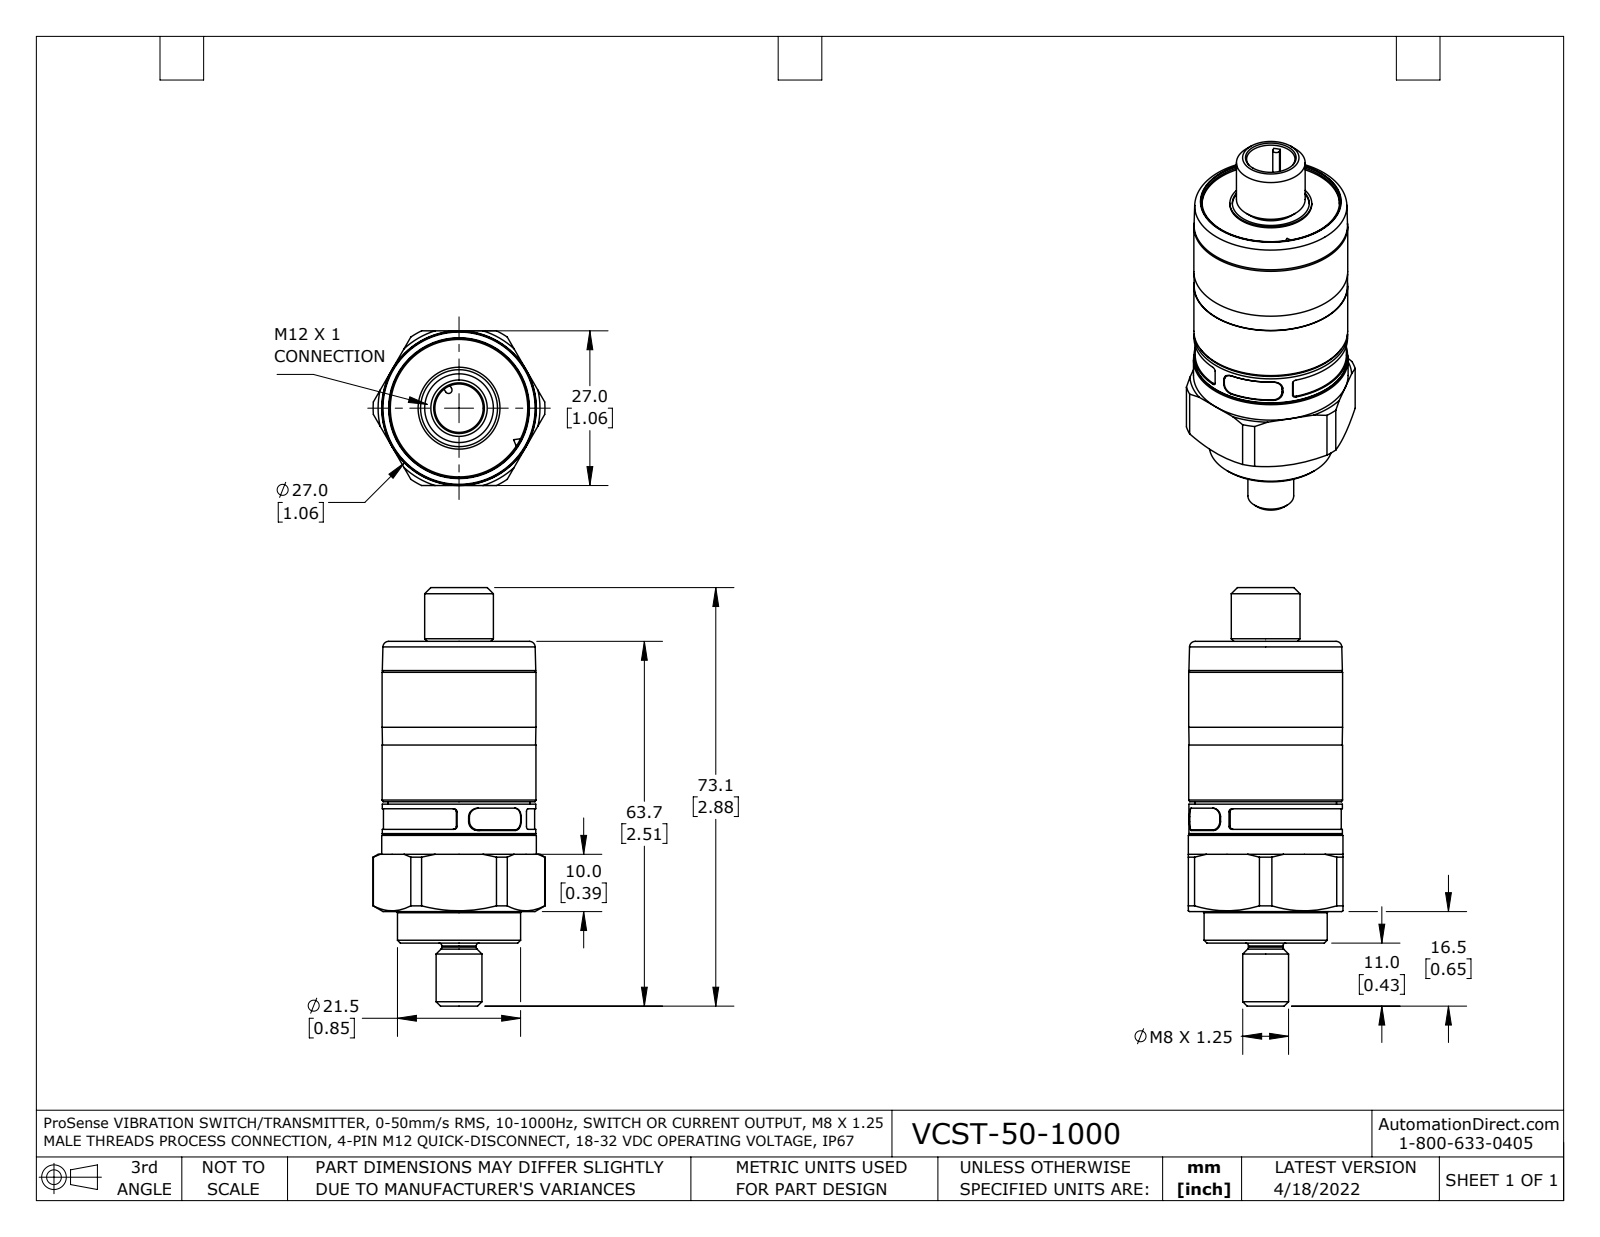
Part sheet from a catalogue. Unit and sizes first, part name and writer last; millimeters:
Units: millimetres
Overall size (bounding box): 73.1 × 30 × 27
Round holes (diameter × count): ⌀8.5 ×1, ⌀13.4 ×1, ⌀24 ×1
Round bosses / shafts (diameter × count): ⌀27 ×1, ⌀26.9 ×1, ⌀26.8 ×1, ⌀26.8 ×1, ⌀26.4 ×1, ⌀24.7 ×1, ⌀21.5 ×1, ⌀14.3 ×1
Partial cylindrical surfaces — rounded edges, fillets, slot ends (radius × count): R1.5 ×8, R0.5 ×4, R0.6 ×1, R13.4 ×1, R15 ×1
Main face-to-face distances: 27, 52.1, 5.5, 46.6, 32.5, 19.7, 14.1, 19.8, 14.2, 32.4
Volume: 29 990 mm³ · Surface area: 7 116 mm²
Bodies: 1 solid, 146 faces (55 planar, 49 cylindrical, 42 other)
Part name (STEP PRODUCT): VCST-50-1000
STEP written by: SolidWorks 2021 (AUTOMOTIVE_DESIGN)
